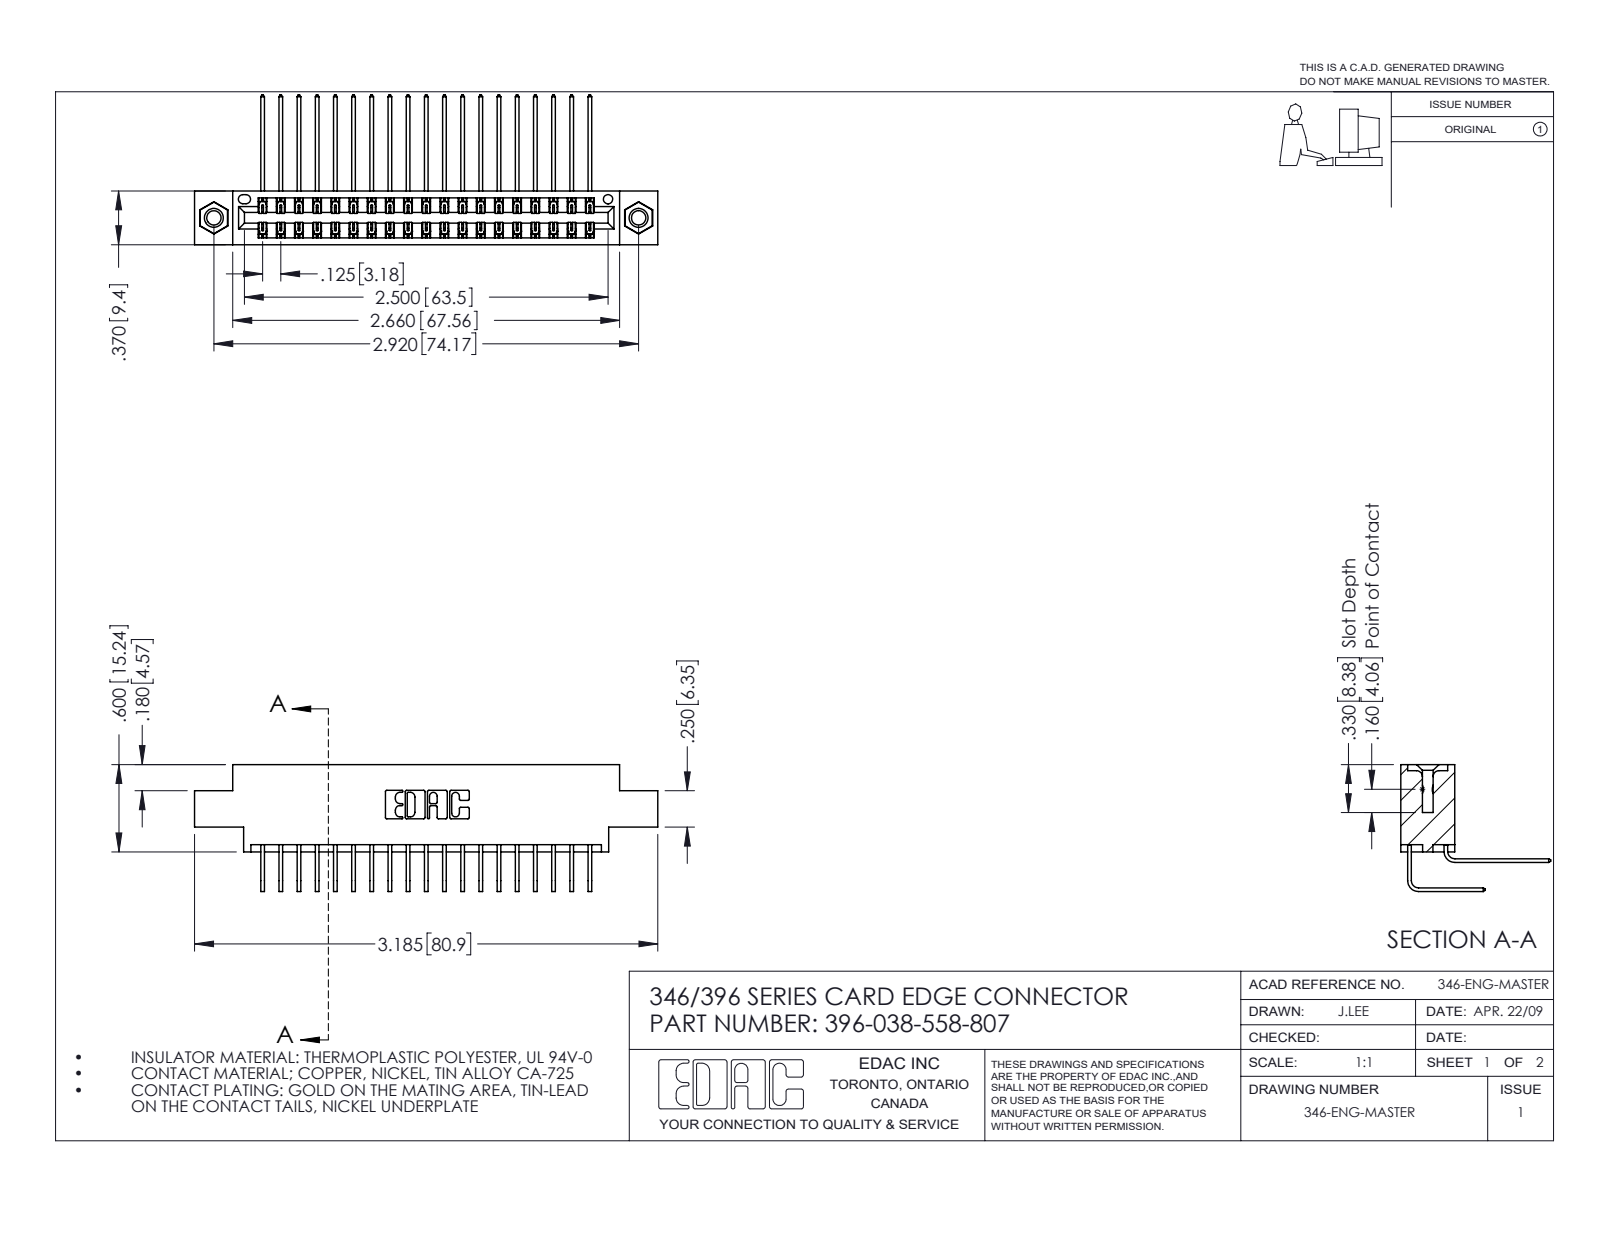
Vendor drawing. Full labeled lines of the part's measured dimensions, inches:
Part name (STEP PRODUCT): 345-250-001_345-250-005-103; 345-292-001_558 Tail - 2; 345-292-001_558 559 Tail - 1; 396-038-558-807 (+1 more)
STEP written by: SolidWorks 2016 (CONFIG_CONTROL_DESIGN)
Units: inches
Bodies: 41 solids, 2238 faces (1518 planar, 704 cylindrical, 16 other)
Overall size (bounding box): 3.185 × 1.03 × 0.873
Volume: 0.474 in³ · Surface area: 17.94 in²
Round holes (diameter × count): ⌀0.098 ×2, ⌀0.125 ×2, ⌀0.156 ×2, ⌀0.064 ×1
Round bosses / shafts (diameter × count): ⌀0.155 ×2
Partial cylindrical surfaces — rounded edges, fillets, slot ends (radius × count): R0.006 ×57, R0.01 ×22, R0.007 ×6, R0.031 ×6, R0.026 ×3, R0.014 ×2, R0.022 ×2, R0.024 ×2
Main face-to-face distances: 0.322, 0.048, 0.37, 0.25, 0.025, 0.298, 0.072, 0.275, 0.222, 0.148
Hole centre spacings: 0.246, 2.713, 2.92
